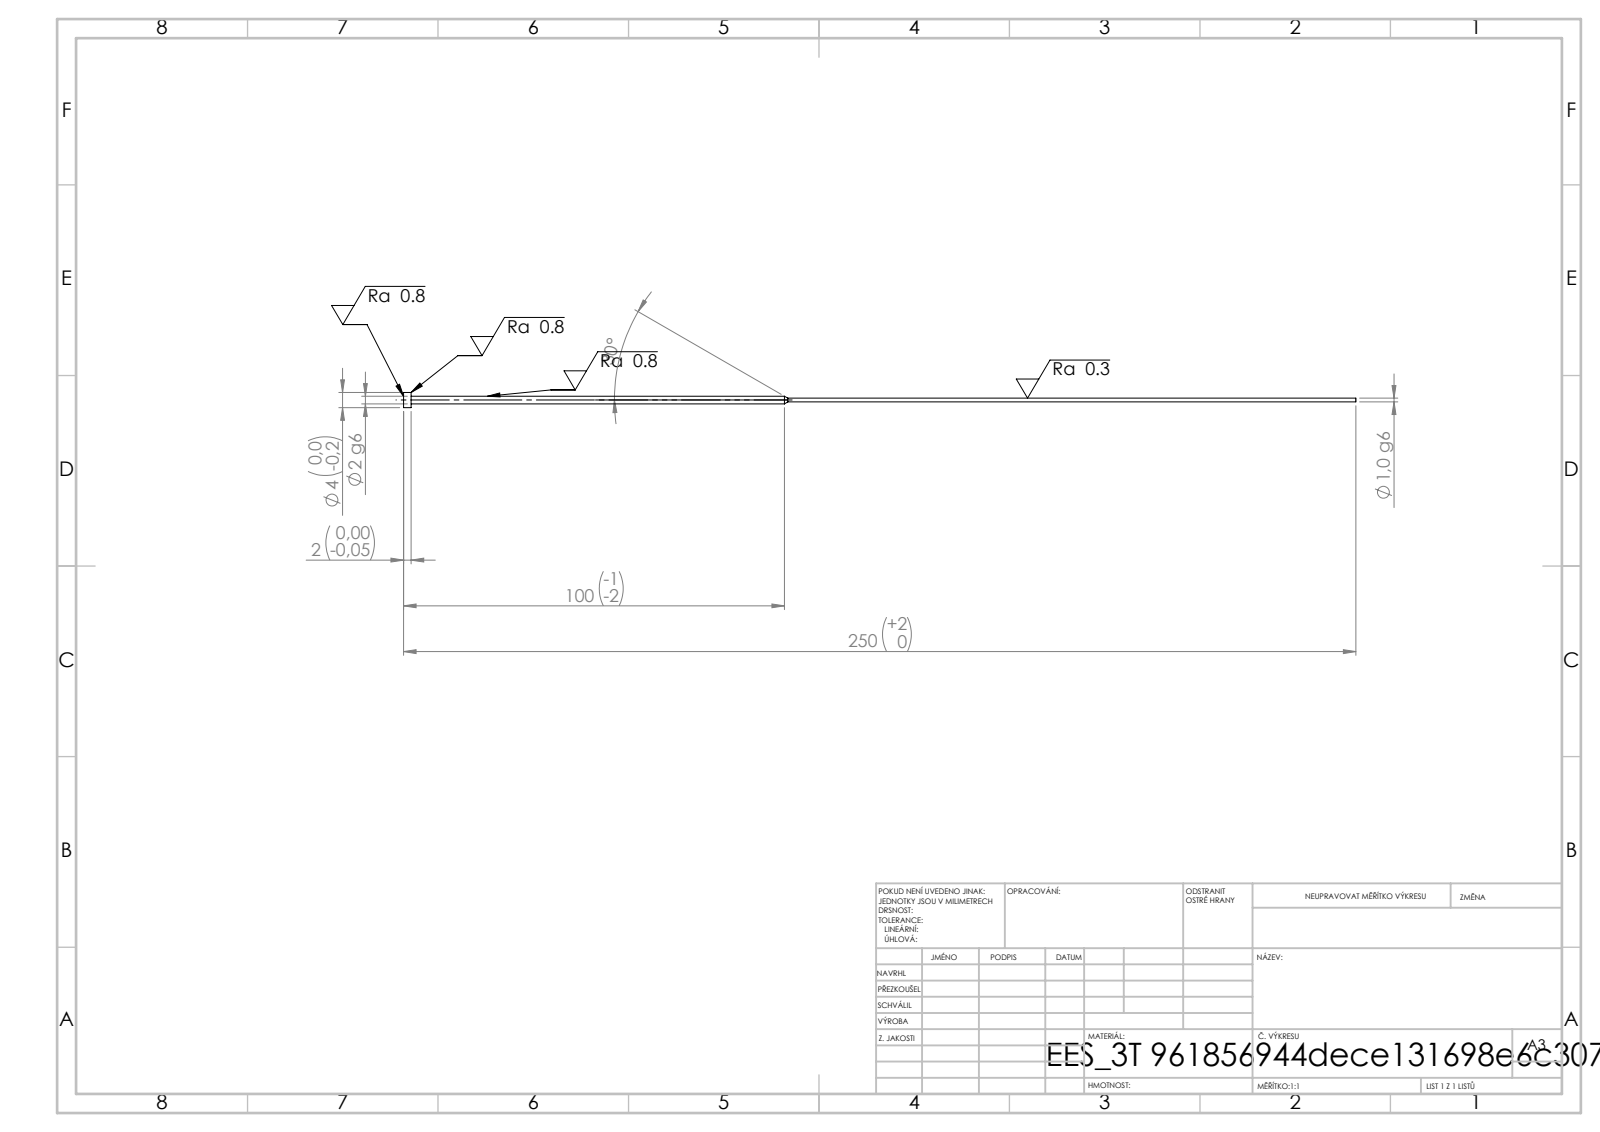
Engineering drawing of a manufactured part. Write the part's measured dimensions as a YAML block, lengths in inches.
step_written_by: "SolidWorks 2019 (CONFIG_CONTROL_DESIGN)"
units: inches
bodies: {solids: 1, faces: 11, planar: 3, cylindrical: 6, other: 2}
overall_size: [9.843, 0.157, 0.157]
volume: 0.028
surface_area: 1.762
round_bosses_or_shafts:
  - {diameter: 0.157, count: 1}
  - {diameter: 0.079, count: 1}
  - {diameter: 0.039, count: 1}
face_to_face_distances: [0.079, 9.764, 9.843]
